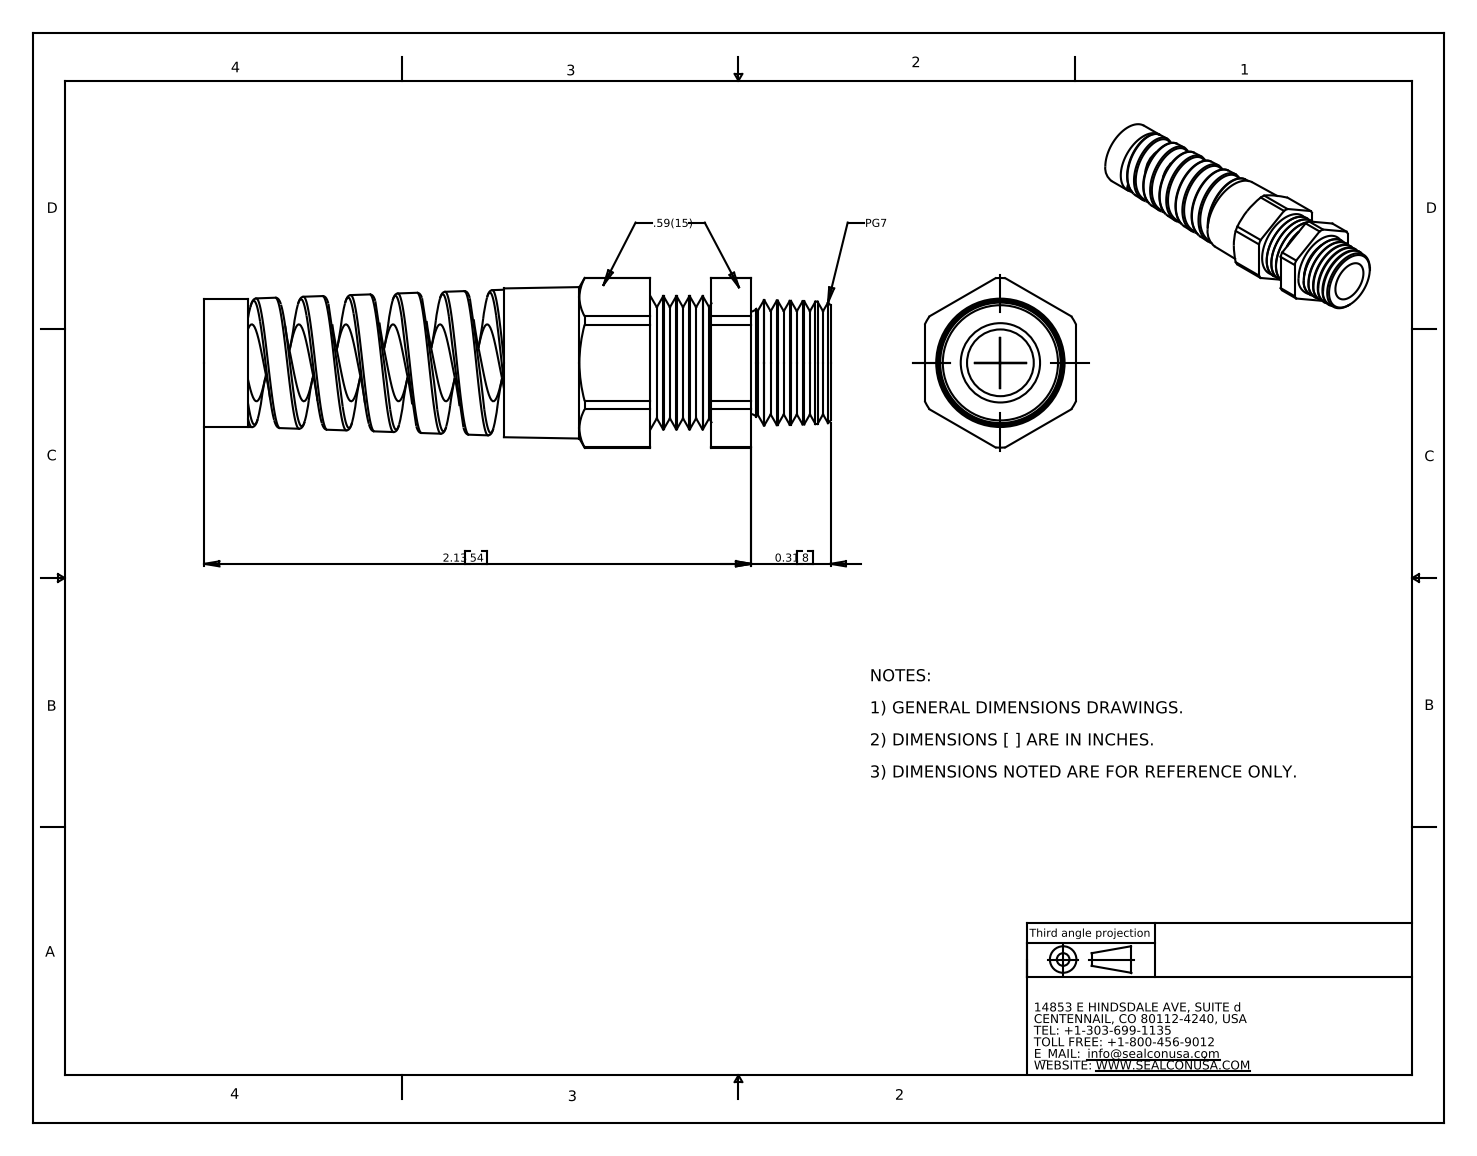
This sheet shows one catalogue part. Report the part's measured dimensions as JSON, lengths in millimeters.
{"part_name": "CF07AA-BK", "step_written_by": "SolidWorks 2007 (CONFIG_CONTROL_DESIGN)", "units": "millimeters", "bodies": {"solids": 1, "faces": 146, "planar": 19, "cylindrical": 39, "other": 88}, "overall_size": [62, 16.8, 15], "volume_mm3": 5360, "surface_area_mm2": 5381, "round_holes": [[6.6, 1], [7.6, 1]], "round_bosses_or_shafts": [[13.2, 1], [12.7, 1]], "partial_cylinders_radius": [[8.4, 1]], "face_to_face_distances": [15, 54.1, 29.6, 24.5, 44.1, 14.5, 10, 50.2, 20.5, 6]}
